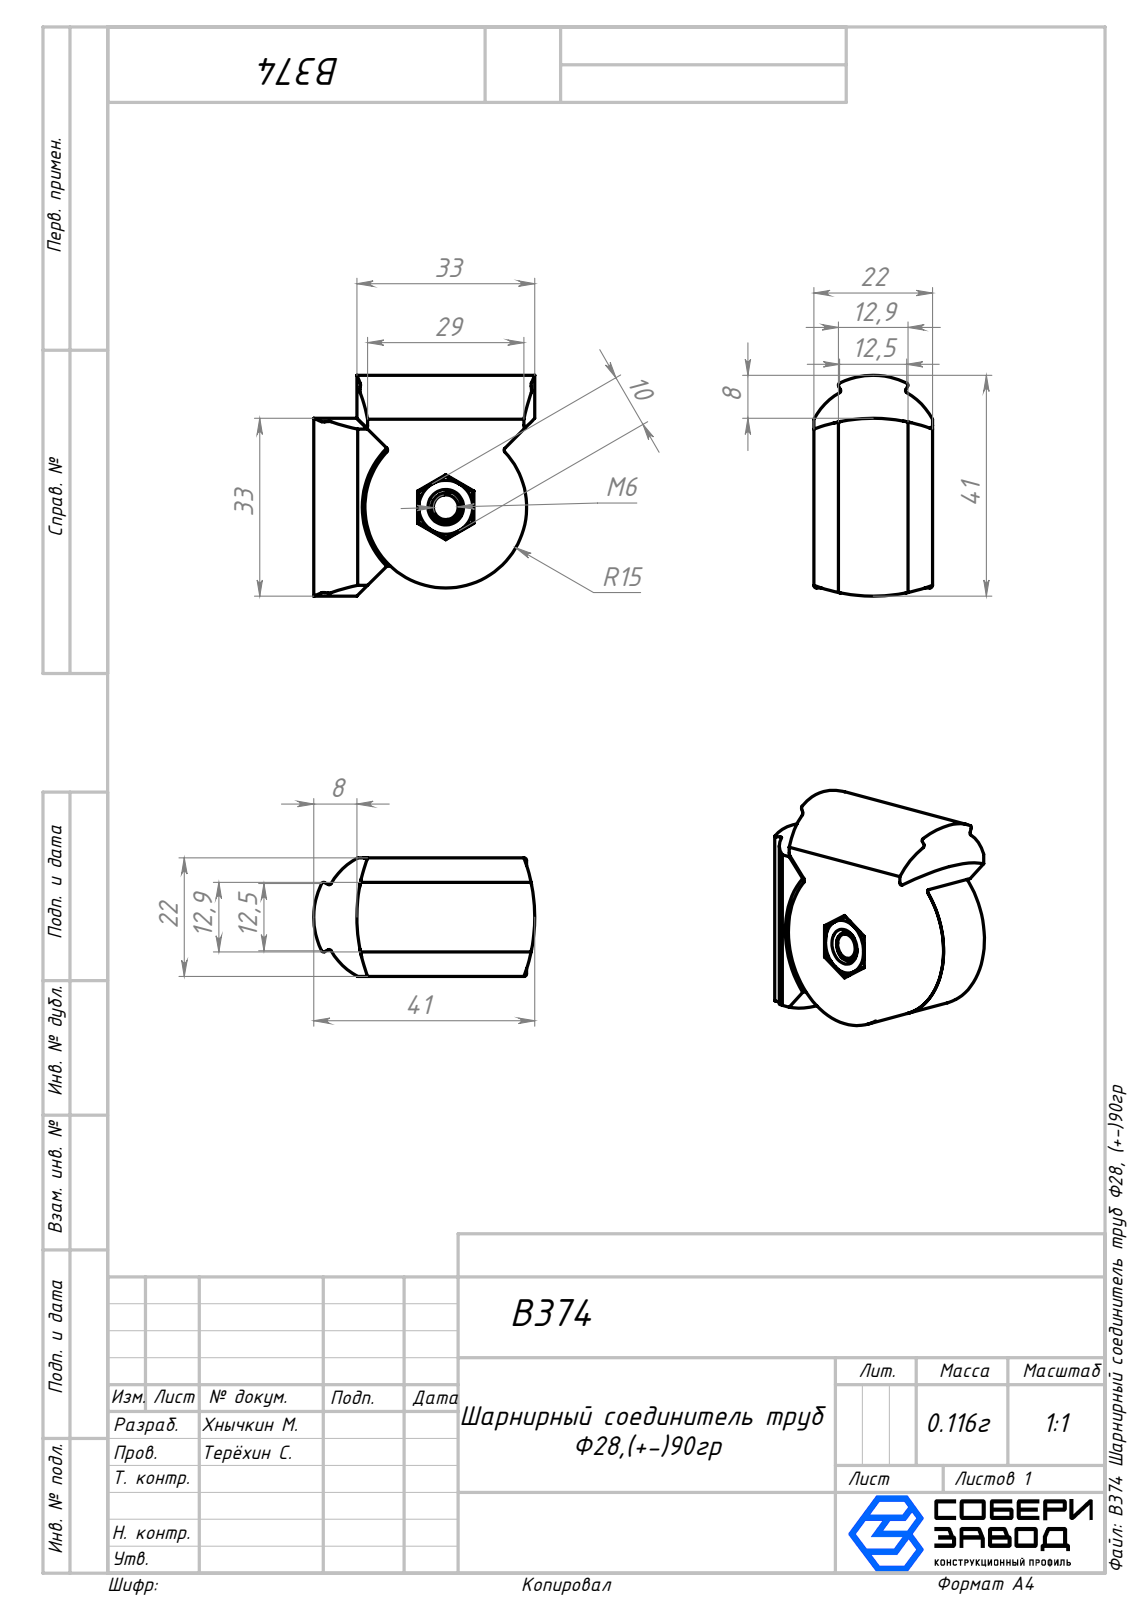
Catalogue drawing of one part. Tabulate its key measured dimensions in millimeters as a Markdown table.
| quantity | value |
| --- | --- |
| part name | Болт_00; B383 Адаптер Ф43х150мм, скользящий и крутящийся по трубе Ф28; Стенка_1_00; Стенка_2_00 (+1 more) |
| STEP written by | SolidWorks 2025 (AUTOMOTIVE_DESIGN) |
| units | millimeters |
| bodies | 4 solids, 240 faces (88 planar, 81 cylindrical, 71 other) |
| overall size | 41.93 × 41 × 28.49 |
| volume | 23 958 mm³ |
| surface area | 12 329 mm² |
| round holes (diameter × count) | 6.5 × 2, 5.2 × 1, 10.2 × 1 |
| round bosses / shafts (diameter × count) | 30 × 1, 10 × 1, 6 × 1 |
| partial cylindrical surfaces (radius × count) | 0.4 × 8, 0.5 × 8, 31.25 × 4, 12.45 × 2, 14 × 2, 15.5 × 1 |
| main face-to-face distances | 22.35, 0.34, 11, 11.01, 11.34, 11.35, 6, 3.18, 7.82, 8.16 |
